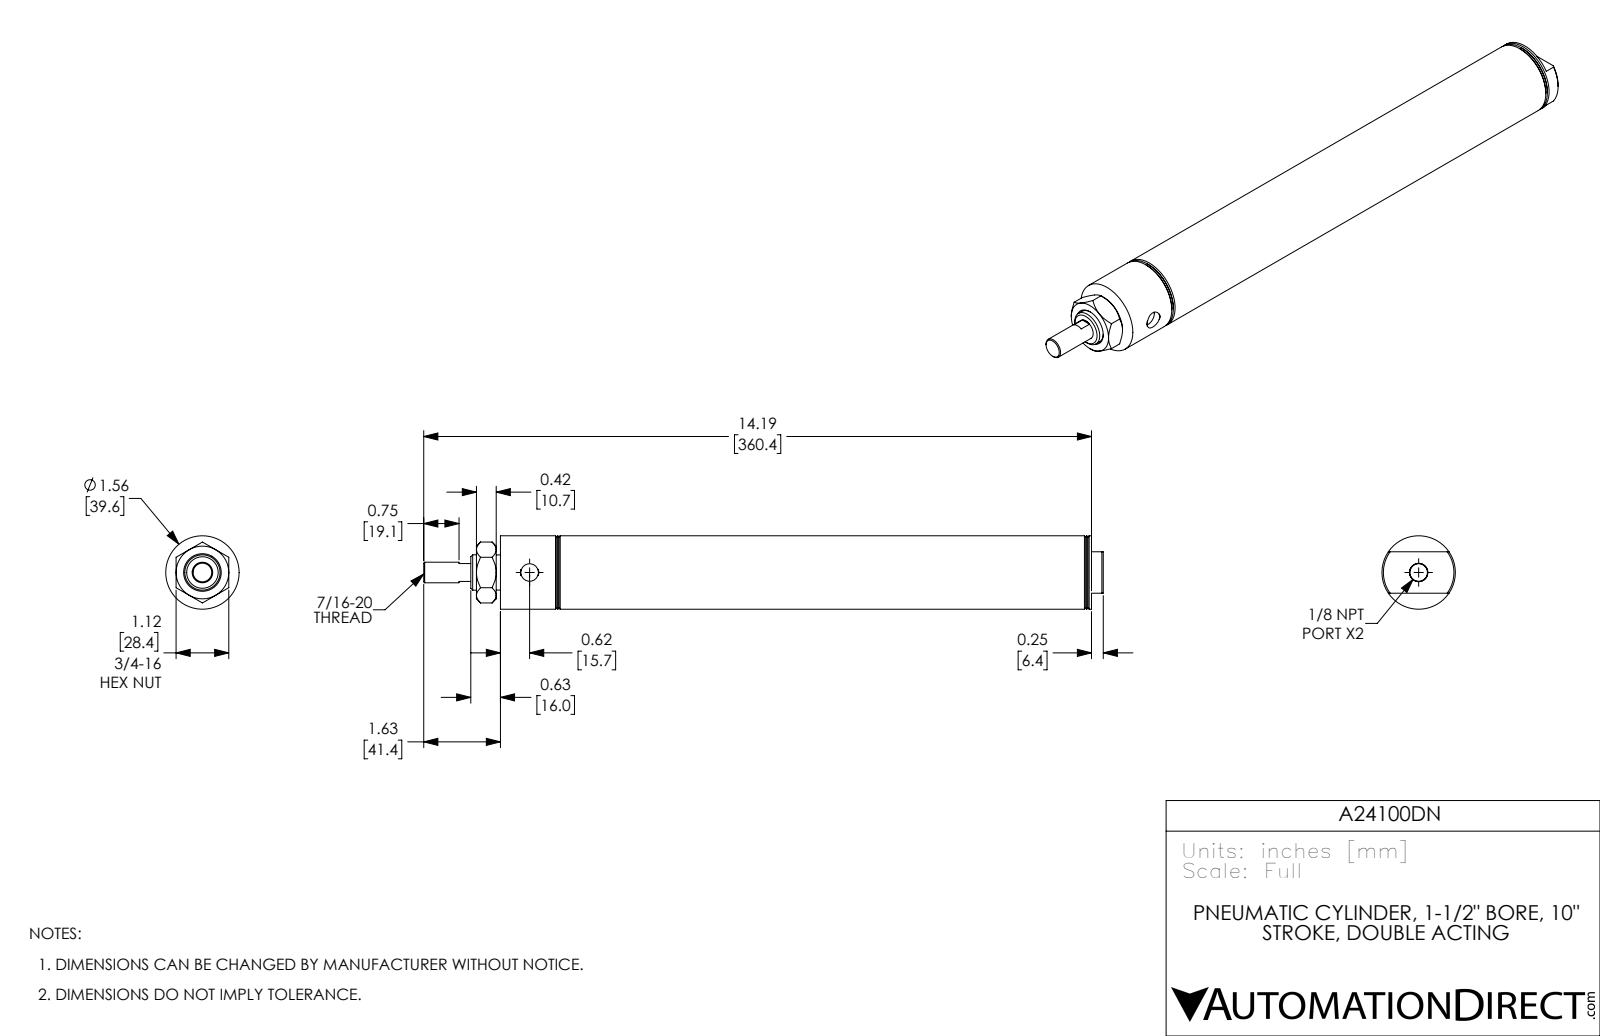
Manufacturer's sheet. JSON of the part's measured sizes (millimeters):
{"part_name": "A24100DN_Mounting Nut_D-3556; A24100DN-Rod; A24100DN-MainBody; A24100DN", "step_written_by": "SolidWorks 2017 (AUTOMOTIVE_DESIGN)", "units": "millimeters", "bodies": {"solids": 3, "faces": 104, "planar": 32, "cylindrical": 24, "other": 48}, "overall_size": [366.8, 39.6, 39.6], "volume_mm3": 144000, "surface_area_mm2": 97740, "round_holes": [[9.5, 2], [11.1, 1], [19.1, 1], [38.1, 1]], "round_bosses_or_shafts": [[39.6, 1], [18.9, 1]], "face_to_face_distances": [12.7, 266.7, 254, 300.7, 288, 34, 24.6, 37.3, 291.3, 325.4]}
